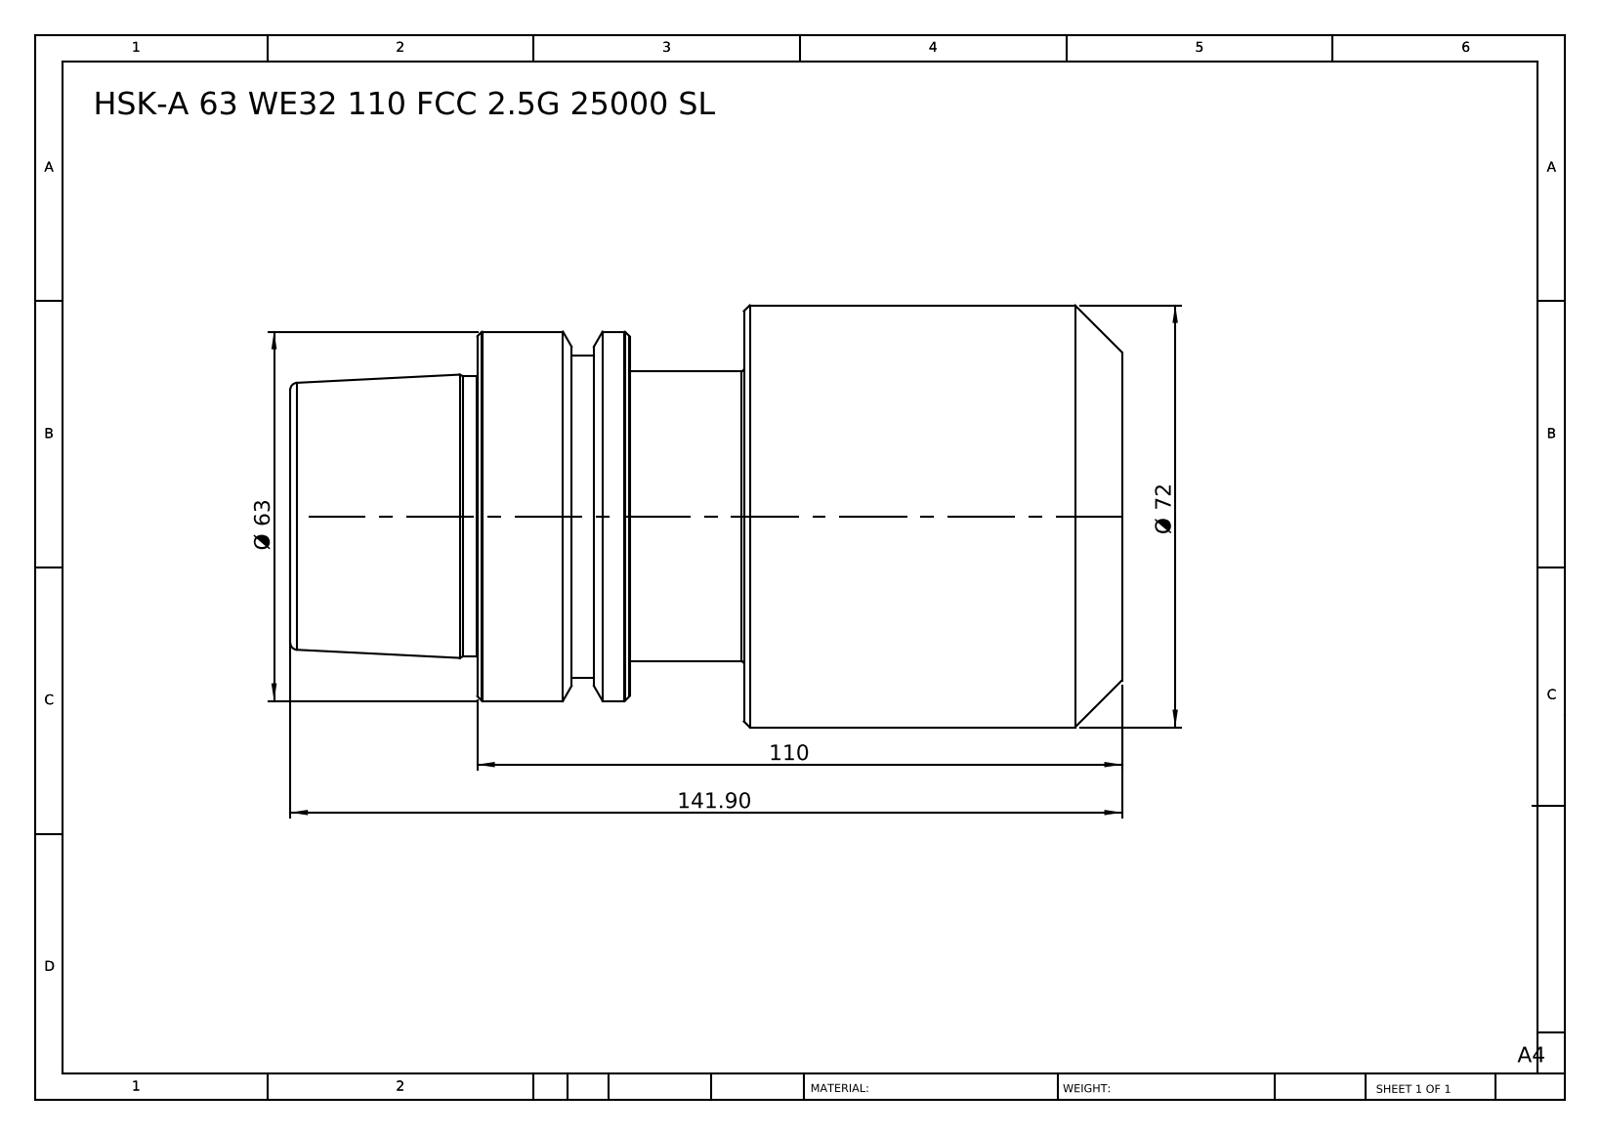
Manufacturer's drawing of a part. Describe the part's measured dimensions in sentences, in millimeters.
The part is named "HSK-A 63 WE32 110 6.3G 20000 SL". Its 3-D file was written by "SolidWorks 2014 (CONFIG_CONTROL_DESIGN)". It is 1 solid with 51 faces: 7 planar, 12 cylindrical and 32 other. Overall it measures 141.9 by 72 by 72 millimeters. Its volume is 425 901 cubic millimeters and its surface area 37 259 square millimeters. Round bosses or shafts: 1 of diameter 72, 1 of diameter 63, 1 of diameter 55, 1 of diameter 49.5, 1 of diameter 47.78. The main face-to-face distances are 64.5, 141.9, 77.4, 84, 19.5, 57.9, 110, 45.5, 26, 31.9.
